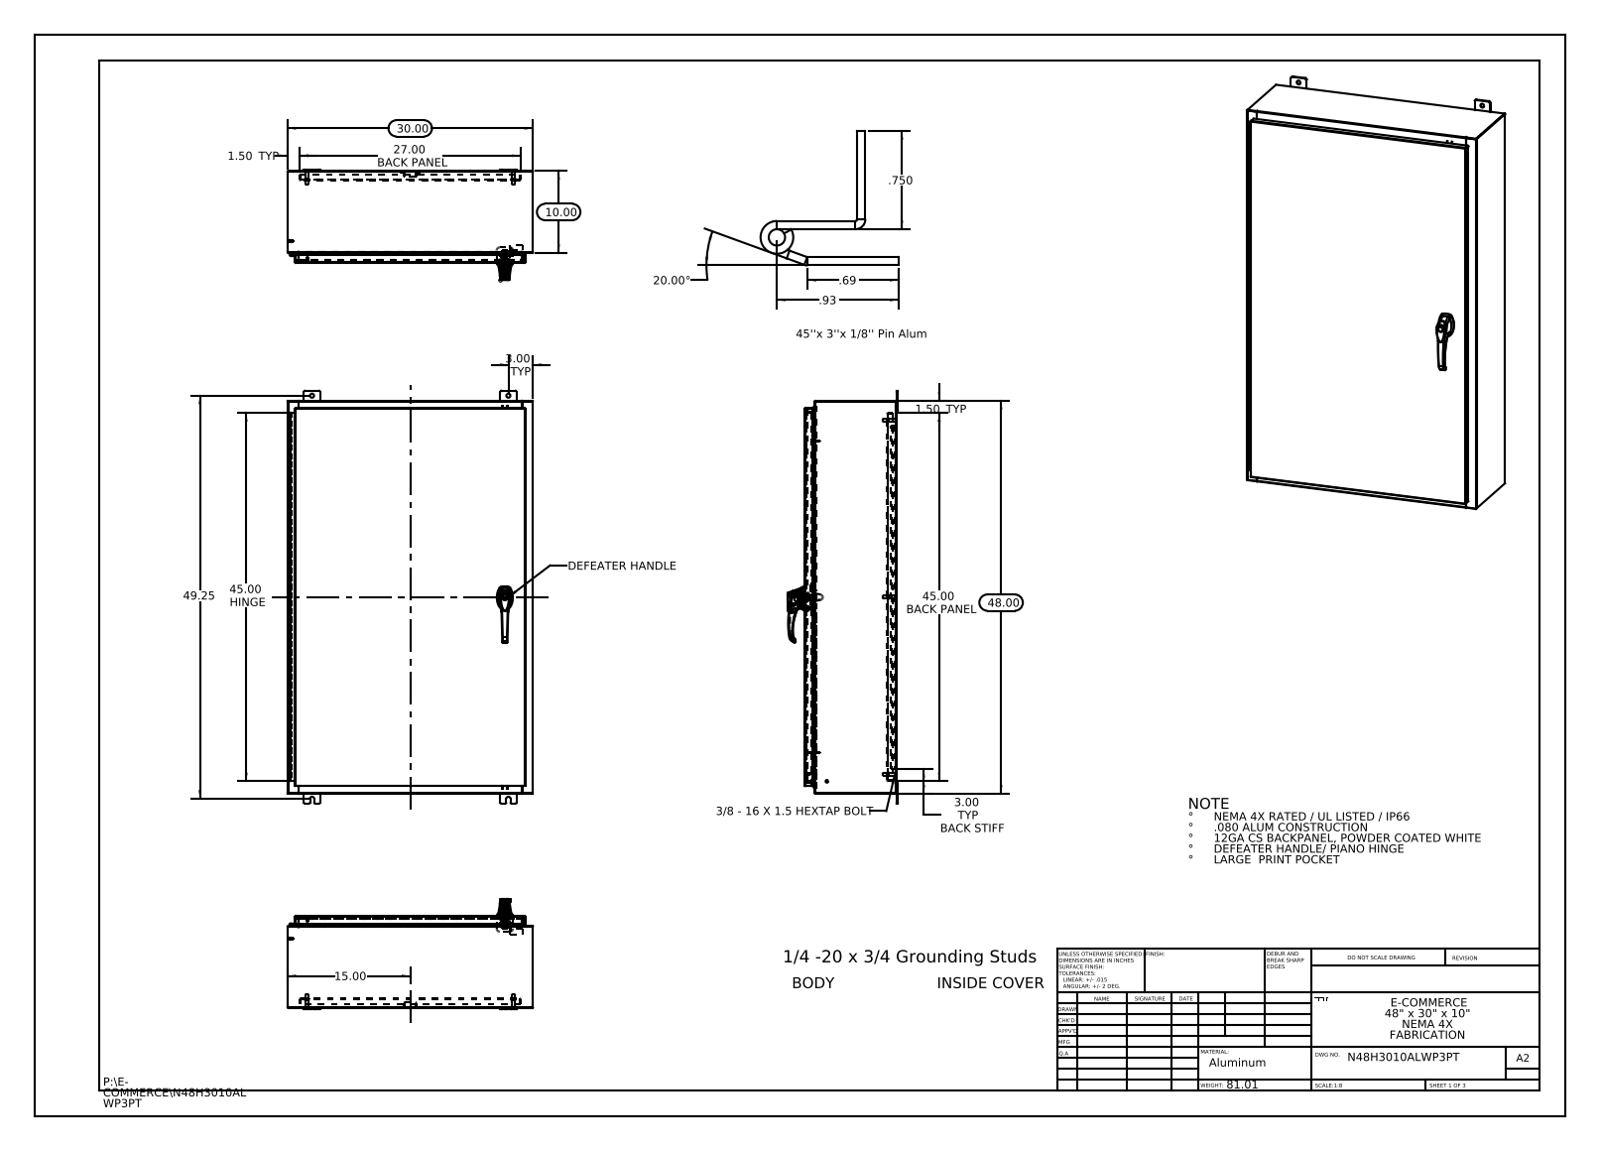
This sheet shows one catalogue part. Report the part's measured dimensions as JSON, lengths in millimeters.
{"part_name": "N48H3010ALWP3PT Body; 10_30 CD Stud; 2616310101; N48H3010ALWP3PT Enclosure Stiffener (+8 more)", "step_written_by": "SolidWorks 2013 (CONFIG_CONTROL_DESIGN)", "units": "millimeters", "bodies": {"solids": 40, "faces": 3182, "planar": 1227, "cylindrical": 1237, "other": 718}, "overall_size": [1282.7, 762, 342.8], "volume_mm3": 8623000, "surface_area_mm2": 8406000, "round_holes": [[12.7, 10], [6.4, 4], [3.5, 3], [4.1, 3], [2, 2], [5.2, 2], [8, 2], [11.1, 2], [3.2, 1], [3.2, 1], [5, 1], [7, 1]], "round_bosses_or_shafts": [[15.9, 6], [9.5, 6], [8.4, 6], [4, 4], [3.6, 4], [8, 3], [6, 3], [30, 1]], "partial_cylinders_radius": [[3, 37], [0.2, 33], [0.3, 28], [4.8, 24], [2.2, 22], [1, 15], [0.7, 12], [0.2, 6]], "face_to_face_distances": [1.9, 282.6, 280.7, 2.6, 284.5, 25.4, 257.2, 27.3, 255.3, 29.9], "hole_center_spacings": [440.9, 499.5, 549.3, 844.4, 641.4, 7.5, 15.9, 21.4]}
